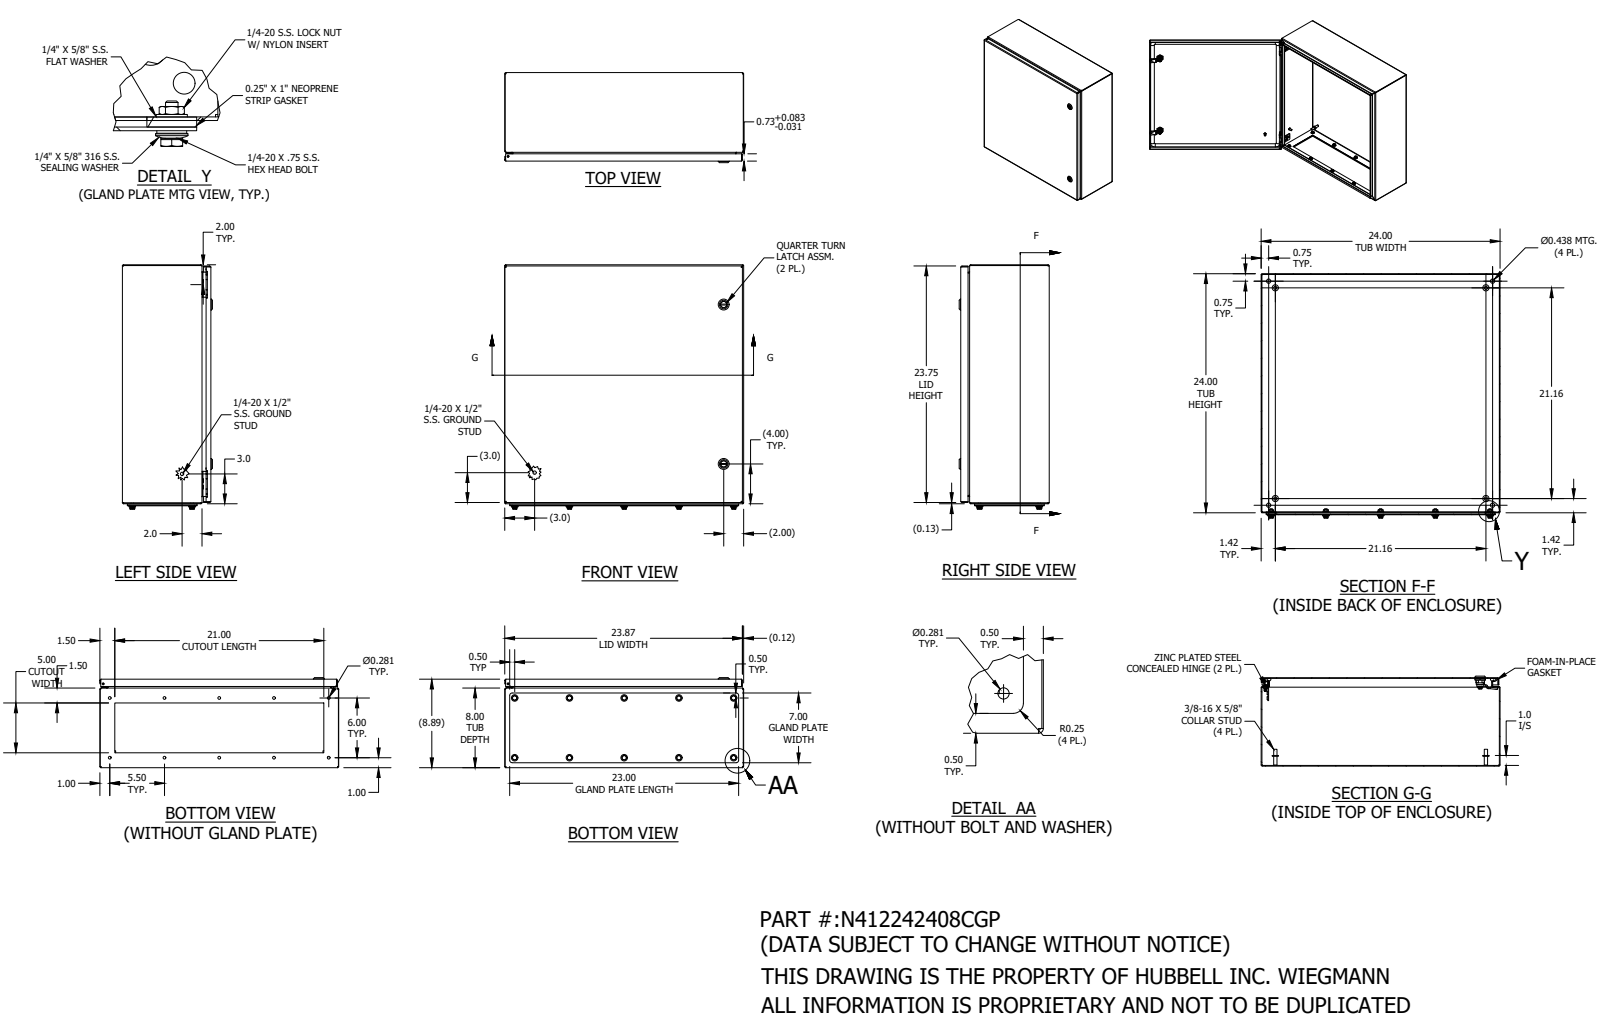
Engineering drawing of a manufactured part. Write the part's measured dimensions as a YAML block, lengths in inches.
part_name: "N412242408CGP"
step_written_by: "SolidWorks 2019 (AUTOMOTIVE_DESIGN)"
units: inches
bodies: {solids: 87, faces: 2561, planar: 1047, cylindrical: 786, other: 728}
overall_size: [24.519, 24, 9.044]
volume: 189.1
surface_area: 4700
round_holes:
  - {diameter: 0.211, count: 10}
  - {diameter: 0.281, count: 10}
  - {diameter: 0.29, count: 10}
  - {diameter: 0.16, count: 8}
  - {diameter: 0.275, count: 7}
  - {diameter: 0.235, count: 6}
  - {diameter: 0.35, count: 6}
  - {diameter: 0.188, count: 5}
  - {diameter: 0.093, count: 4}
  - {diameter: 0.167, count: 4}
  - {diameter: 0.235, count: 4}
  - {diameter: 0.437, count: 4}
round_bosses_or_shafts:
  - {diameter: 0.25, count: 20}
  - {diameter: 0.625, count: 12}
  - {diameter: 0.65, count: 10}
  - {diameter: 0.6, count: 10}
  - {diameter: 0.438, count: 10}
  - {diameter: 0.36, count: 4}
  - {diameter: 0.33, count: 4}
  - {diameter: 0.32, count: 4}
partial_cylinders:
  - {radius: 0.012, count: 56}
  - {radius: 0.05, count: 26}
  - {radius: 0.02, count: 21}
  - {radius: 0.047, count: 20}
  - {radius: 0.121, count: 20}
  - {radius: 0.157, count: 9}
  - {radius: 0.125, count: 8}
  - {radius: 0.13, count: 8}
face_to_face_distances: [0.074, 8.812, 8.738, 8.886, 23.926, 0.074, 24.13, 23.852, 24.056, 24]
hole_center_spacings: [5.5, 6, 11, 8.139, 12.53, 16.5, 0.66, 5.5]
